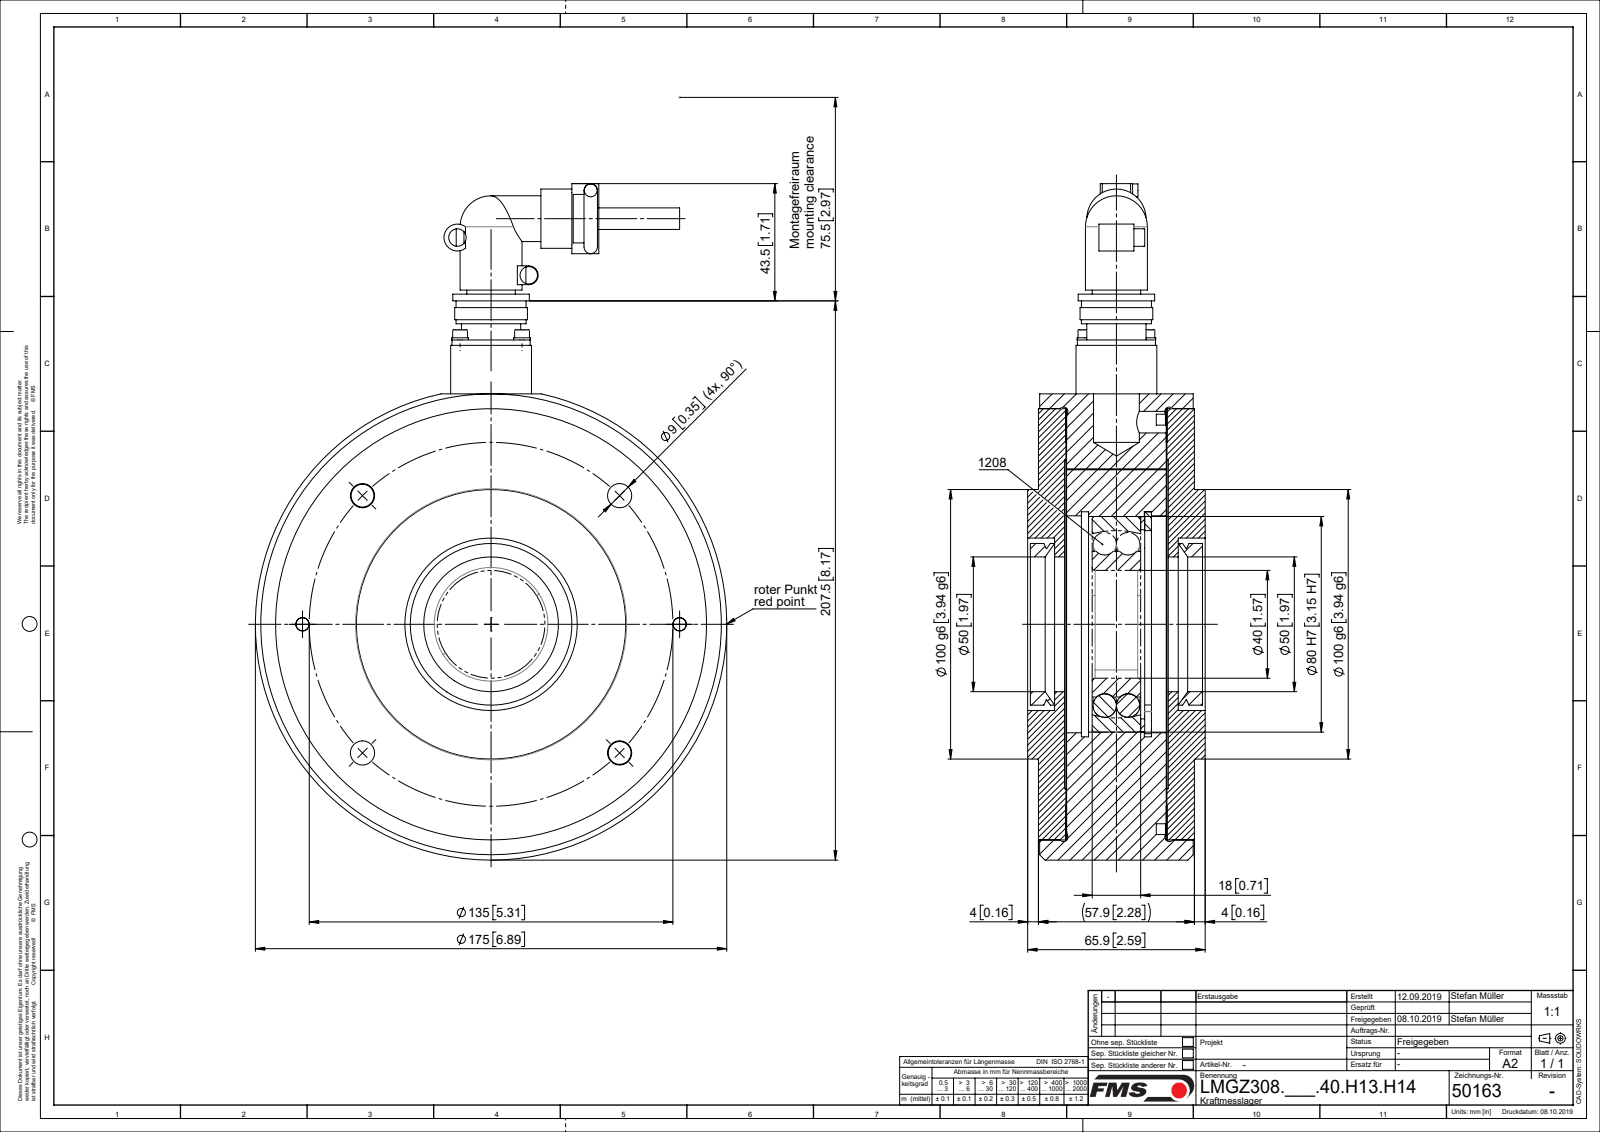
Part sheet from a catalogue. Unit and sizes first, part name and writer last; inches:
Units: inches
Overall size (bounding box): 9.882 × 6.89 × 2.594
Round holes (diameter × count): ⌀0.102 ×4, ⌀0.126 ×4, ⌀0.134 ×4, ⌀0.138 ×4, ⌀0.354 ×4, ⌀0.203 ×2, ⌀0.26 ×2, ⌀0.433 ×2, ⌀0.906 ×1, ⌀1.575 ×1, ⌀1.89 ×1, ⌀1.969 ×1
Round bosses / shafts (diameter × count): ⌀0.244 ×4, ⌀0.217 ×4, ⌀0.118 ×4, ⌀0.866 ×2, ⌀0.394 ×2, ⌀0.256 ×2, ⌀0.236 ×2, ⌀0.189 ×2
Partial cylindrical surfaces — rounded edges, fillets, slot ends (radius × count): R0.098 ×2, R0.295 ×2, R0.138 ×1, R0.197 ×1
Main face-to-face distances: 1.467, 0.402, 0.411, 1.868, 1.878, 1.457, 1.476, 0.02, 1.496, 0.382
Hole centre spacings: 0.64, 0.906, 2.074, 2.657, 3.758, 5.002, 1.281, 2.756
Volume: 78.05 in³ · Surface area: 431.6 in²
Bodies: 23 solids, 415 faces (115 planar, 241 cylindrical, 59 other)
Part name (STEP PRODUCT): L50163; L4857104; TEIL1; L49026 (+8 more)
STEP written by: Mechanical Desktop 2007 (CONFIG_CONTROL_DESIGN)
